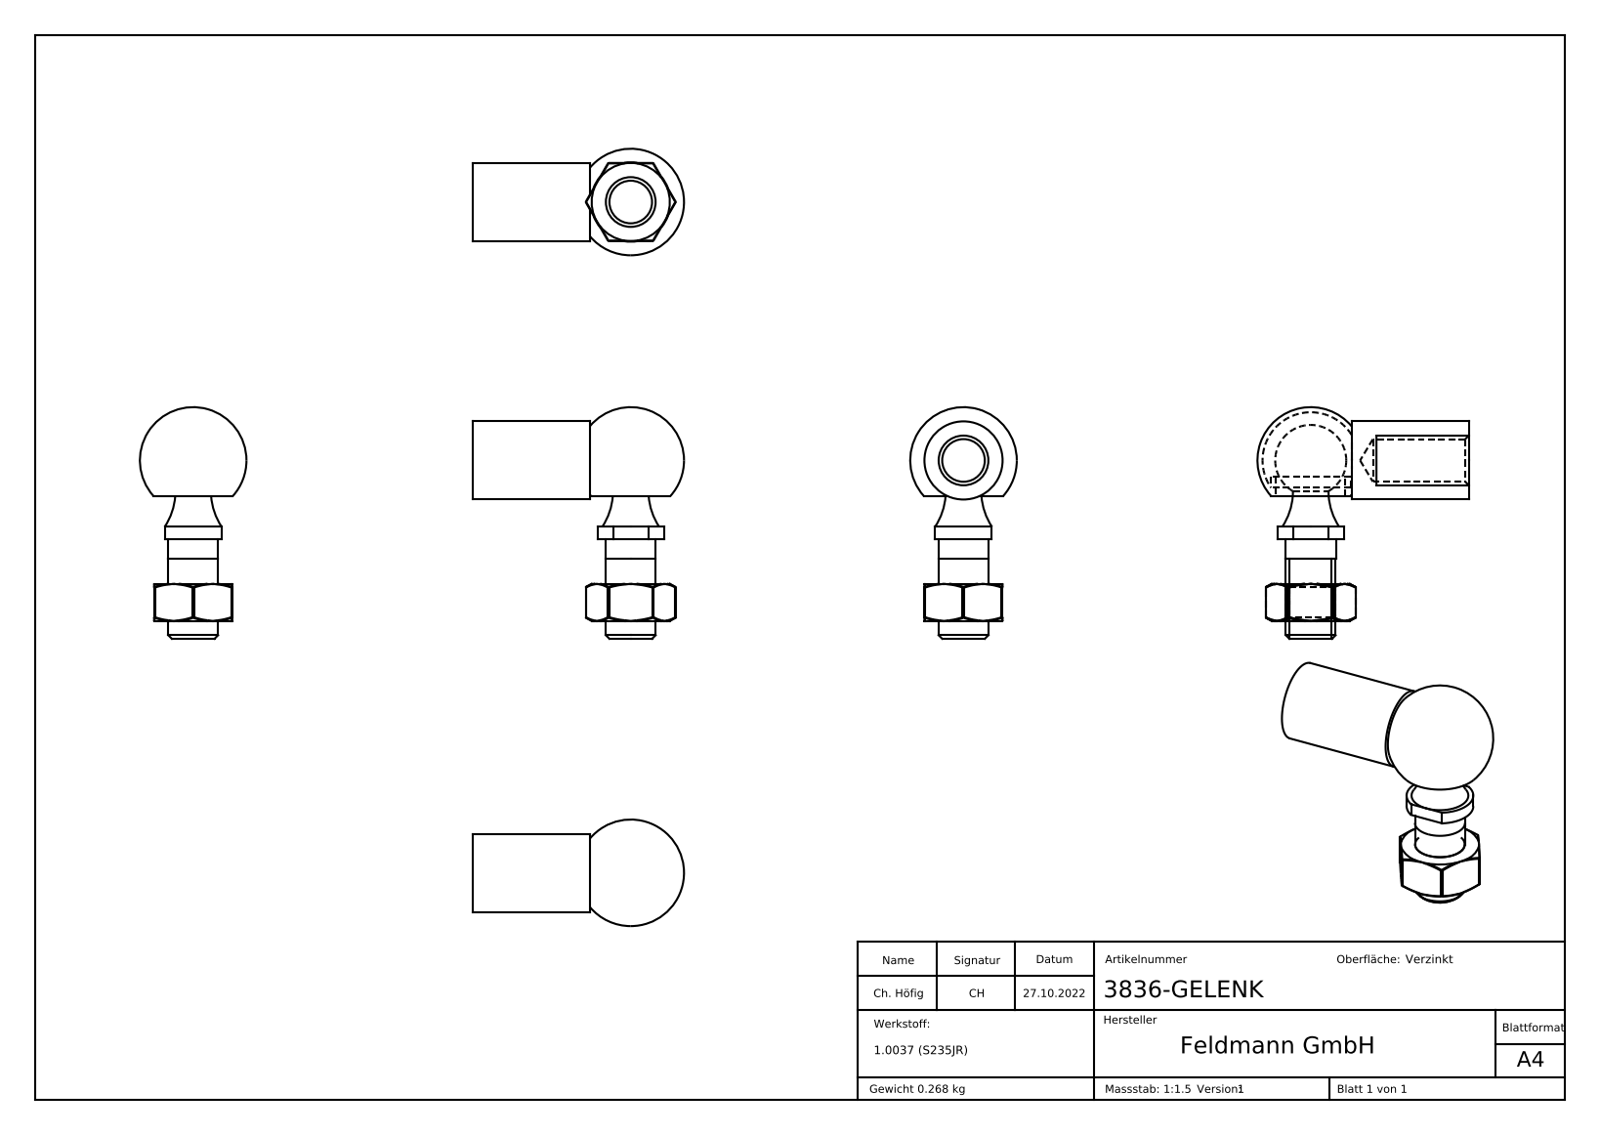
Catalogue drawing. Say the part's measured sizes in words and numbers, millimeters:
The part is named "3836-GELENK Teil2_3836-GELENK Teil2; 3836-GELENK Teil1_3836-GELENK Teil1; 3836-GELENK Teil4_3836-GELENK Teil4; 3836-GELENK". Its 3-D file was written by "SolidWorks 2018 (CONFIG_CONTROL_DESIGN)". It is 3 solids with 417 faces: 190 planar, 15 cylindrical and 212 other. Overall it measures 65.21 by 59.5 by 30 millimeters. Its volume is 26 092 cubic millimeters and its surface area 13 345 square millimeters. Round holes: 2 of diameter 12, 1 of diameter 19.5. Round bosses or shafts: 1 of diameter 22.36, 1 of diameter 22, 1 of diameter 14.1, 1 of diameter 14. Partial cylindrical surfaces (rounded edges, fillets, slot ends): 6 of radius 0.5, 1 of radius 9.4. The main face-to-face distances are 22, 10.5, 33, 5, 15.5, 28.05, 23.05, 12.55, 40.21, 35.21.
